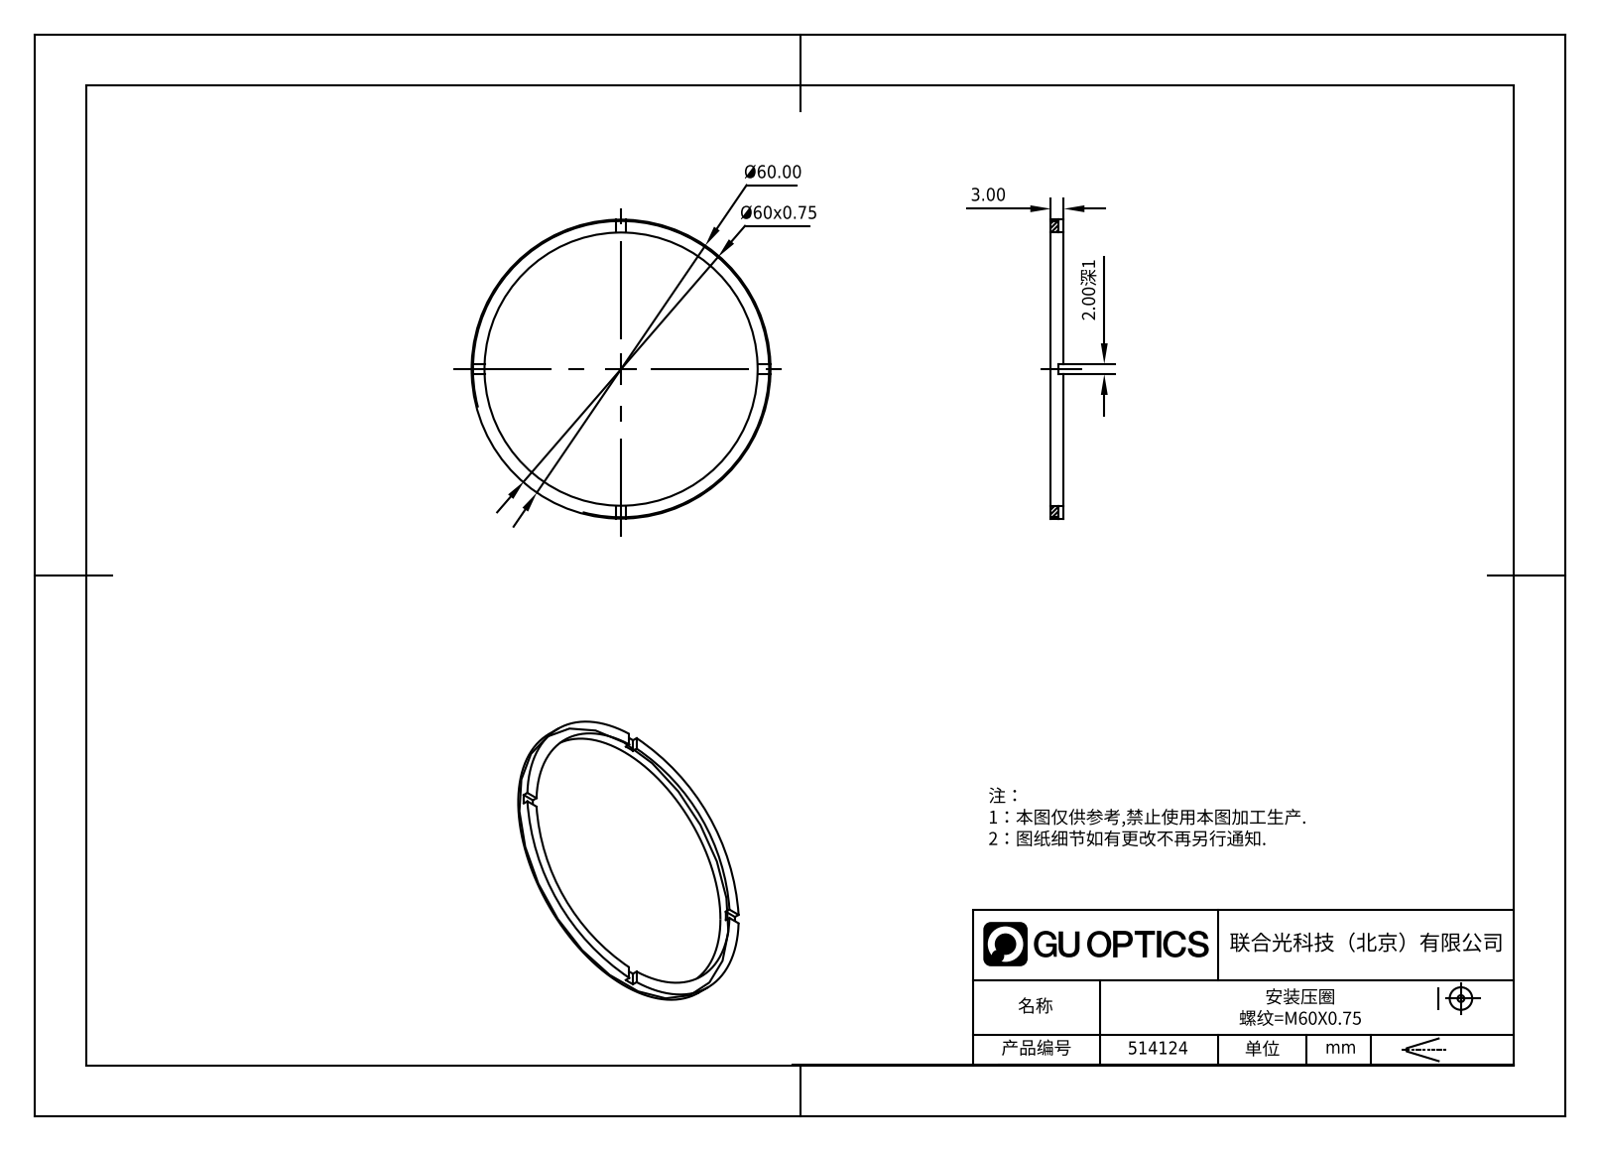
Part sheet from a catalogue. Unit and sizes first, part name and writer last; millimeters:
Units: millimetres
Overall size (bounding box): 60 × 60 × 3
Round holes (diameter × count): ⌀55 ×1
Round bosses / shafts (diameter × count): ⌀60 ×1
Main face-to-face distances: 3, 2, 1
Volume: 1 335 mm³ · Surface area: 1 991 mm²
Bodies: 1 solid, 21 faces (17 planar, 4 cylindrical, 0 other)
Part name (STEP PRODUCT): 514124
STEP written by: SolidWorks 2020 (CONFIG_CONTROL_DESIGN)
